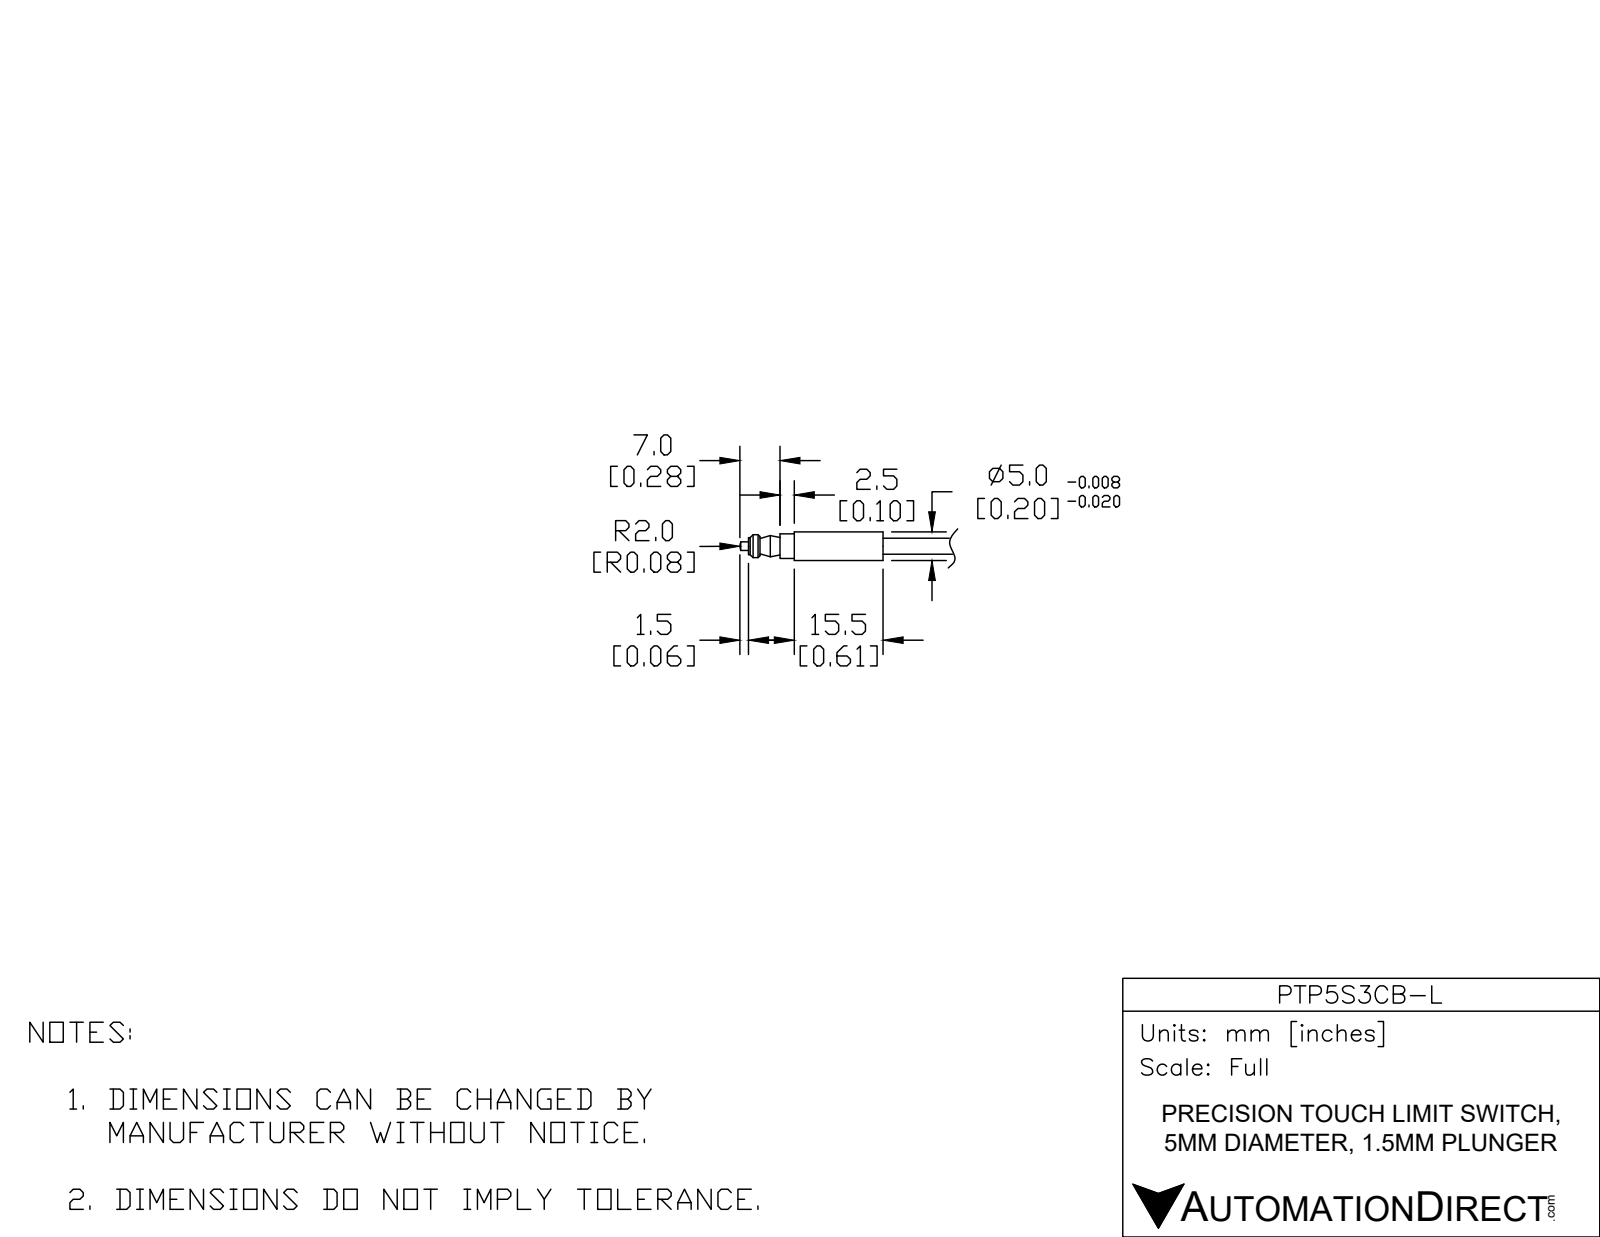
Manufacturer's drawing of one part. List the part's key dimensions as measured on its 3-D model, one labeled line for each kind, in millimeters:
STEP written by: Spatial InterOp 3D (CONFIG_CONTROL_DESIGN)
Units: millimetres
Bodies: 1 solid, 42 faces (8 planar, 16 cylindrical, 18 other)
Overall size (bounding box): 180 × 5 × 5
Volume: 1 592 mm³ · Surface area: 1 906 mm²
Round bosses / shafts (diameter × count): ⌀5 ×1, ⌀4.5 ×1, ⌀4.3 ×1, ⌀4 ×1, ⌀3 ×1, ⌀2.8 ×1, ⌀1.5 ×1
Main face-to-face distances: 120, 145, 25, 18, 138, 163, 173, 155, 35, 10
